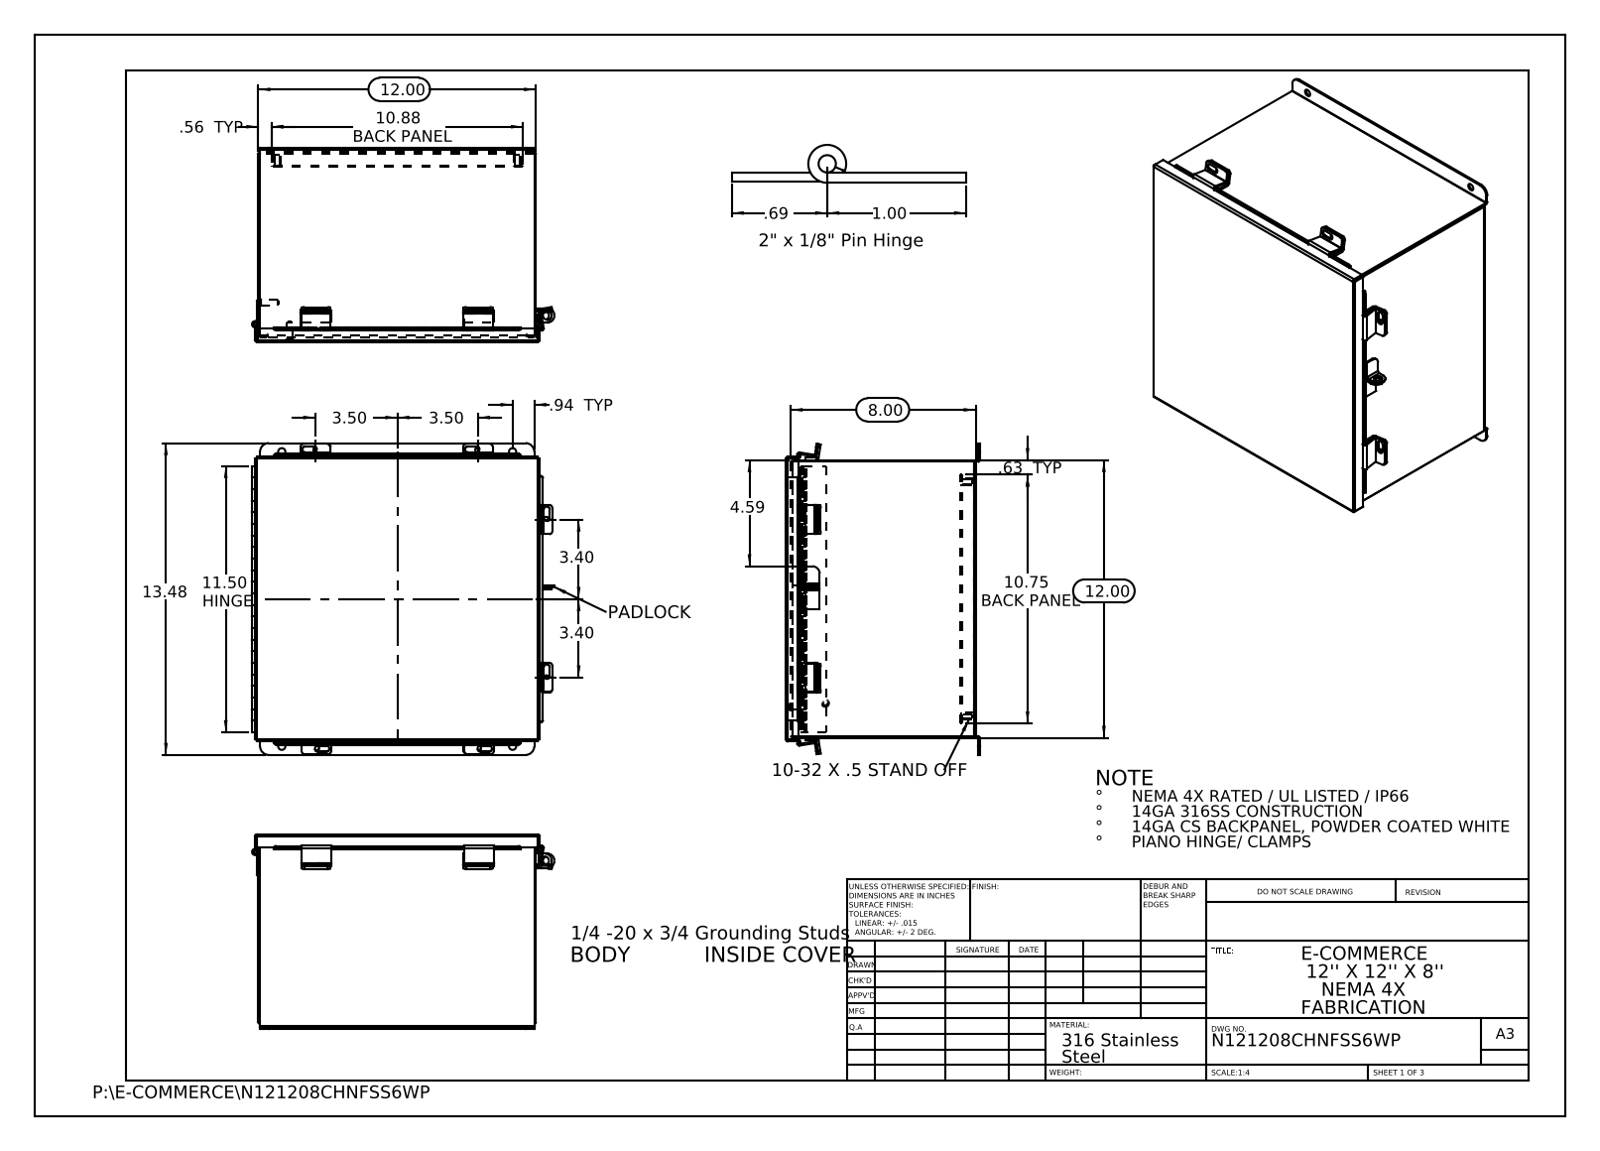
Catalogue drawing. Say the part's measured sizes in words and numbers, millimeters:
The part is named "N121208CHNFSS6WP JIC Cover Clamp; HW-CLH-JH-20104; N121208CHNFSS6WP JIC Enclosure Template; N121208CHNFSS6WP Hinge Body Side (+8 more)". Its 3-D file was written by "SolidWorks 2013 (CONFIG_CONTROL_DESIGN)". It is 27 solids with 794 faces: 499 planar, 275 cylindrical and 20 other. Overall it measures 342.3 by 332 by 213.1 millimeters. Its volume is 1 097 000 cubic millimeters and its surface area 1 177 000 square millimeters. Round holes: 10 of diameter 6.4, 4 of diameter 4.7, 4 of diameter 7.9, 1 of diameter 3.2, 1 of diameter 3.2, 1 of diameter 9.5, 1 of diameter 9.5. Round bosses or shafts: 4 of diameter 8, 2 of diameter 8, 2 of diameter 6, 1 of diameter 6.9, 1 of diameter 6.4. Partial cylindrical surfaces (rounded edges, fillets, slot ends): 21 of radius 3.2, 13 of radius 0.3, 12 of radius 0.2, 12 of radius 2.2, 12 of radius 3.4, 6 of radius 2.1, 6 of radius 2.5, 4 of radius 9.5. The main face-to-face distances are 1.9, 302.9, 206.5, 301, 304.8, 204.5, 208.4, 1.9, 14.6, 12.7. The hole center spacings are 33.4, 260.6, 290.3, 388.6, 177.8, 253.4, 257.2, 263.5.
